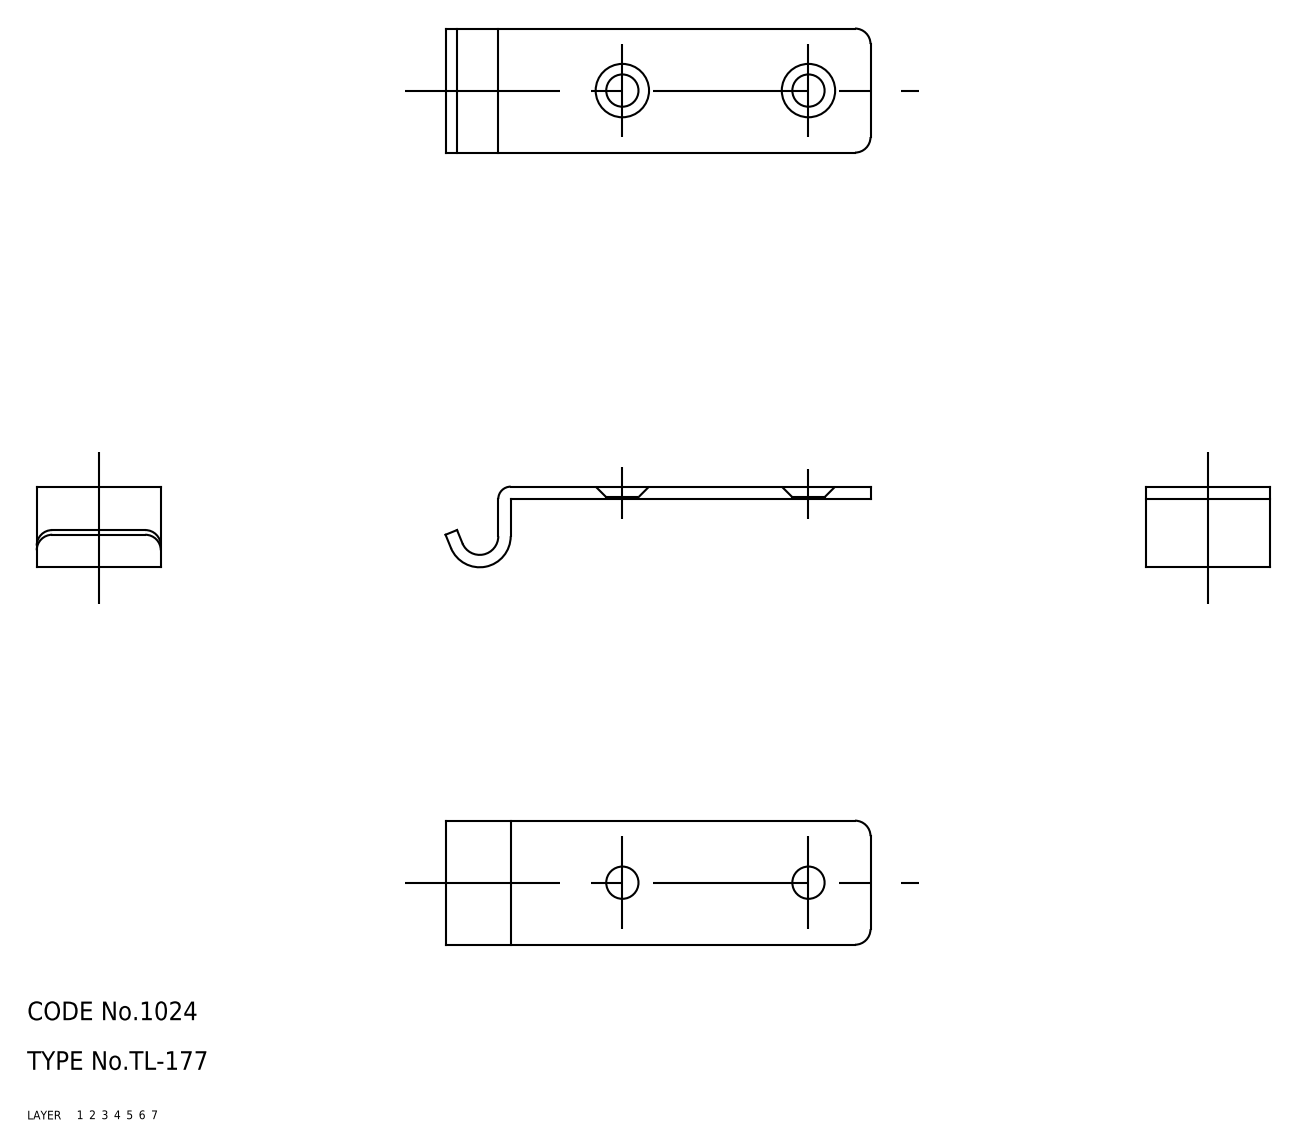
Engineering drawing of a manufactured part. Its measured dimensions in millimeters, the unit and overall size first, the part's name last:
Units: millimetres
Overall size (bounding box): 68.5 × 20 × 13
Volume: 3 002 mm³ · Surface area: 3 487 mm²
Bodies: 1 solid, 25 faces (0 planar, 0 cylindrical, 25 other)
Part name (STEP PRODUCT): keeper
STEP written by: CADfix (AUTOMOTIVE_DESIGN)
